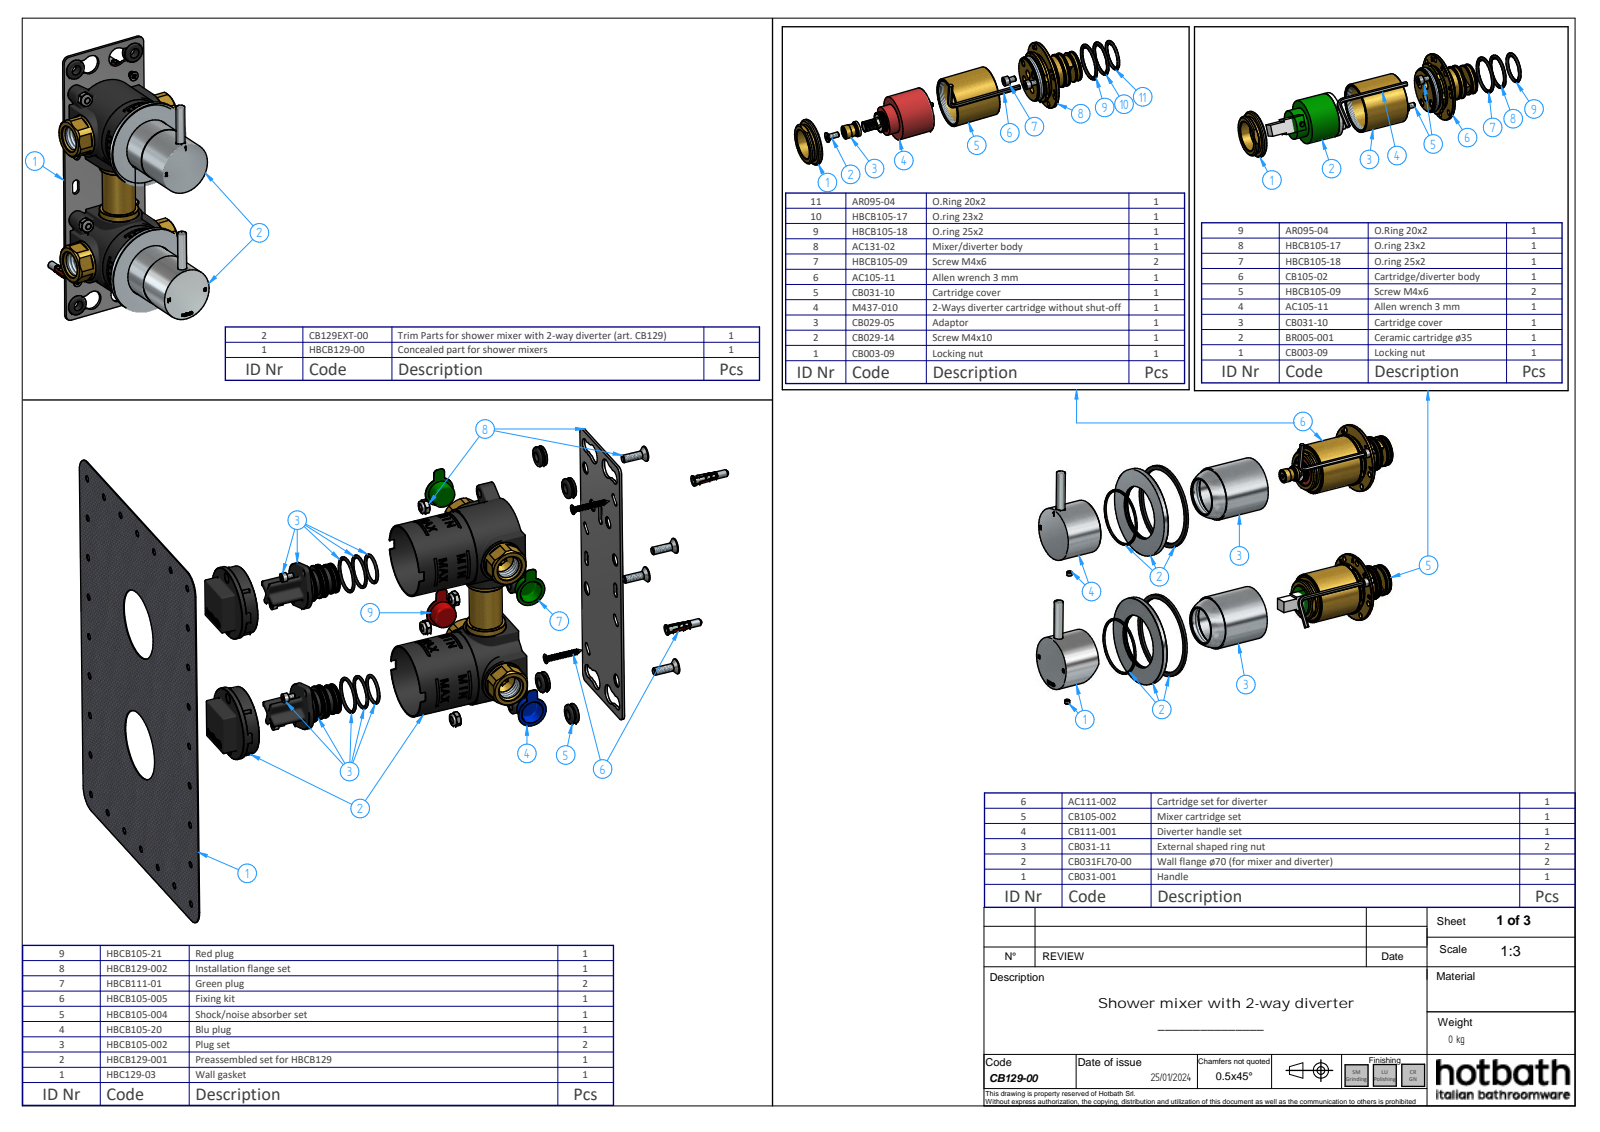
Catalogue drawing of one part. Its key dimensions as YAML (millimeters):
part_name: "CB129EXT-00; CB111-001_oa_0; CB111-02; CB005-08 (+8 more)"
step_written_by: "Solid Edge (AUTOMOTIVE_DESIGN)"
units: millimeters
bodies: {solids: 8, faces: 290, planar: 140, cylindrical: 57, other: 93}
overall_size: [196.43, 72, 70.07]
volume: 58090
surface_area: 65058
round_holes:
  - {diameter: 5, count: 3}
  - {diameter: 30.38, count: 2}
  - {diameter: 36, count: 2}
  - {diameter: 39, count: 2}
  - {diameter: 39.5, count: 2}
  - {diameter: 42.5, count: 2}
  - {diameter: 43, count: 2}
  - {diameter: 44.8, count: 2}
  - {diameter: 57.5, count: 2}
  - {diameter: 66.5, count: 2}
  - {diameter: 3.24, count: 1}
  - {diameter: 3.3, count: 1}
round_bosses_or_shafts:
  - {diameter: 70, count: 2}
  - {diameter: 59.5, count: 2}
  - {diameter: 48.5, count: 2}
  - {diameter: 42, count: 2}
  - {diameter: 7, count: 2}
  - {diameter: 38, count: 1}
  - {diameter: 35, count: 1}
  - {diameter: 17, count: 1}
partial_cylinders:
  - {radius: 5, count: 2}
  - {radius: 0.49, count: 1}
  - {radius: 9, count: 1}
  - {radius: 19, count: 1}
face_to_face_distances: [2, 2.3, 1.8, 3.8, 1.5, 1.7, 4, 50.7, 52.7, 53]
hole_center_spacings: [0.9, 9, 8.1, 9.9, 109.93]
